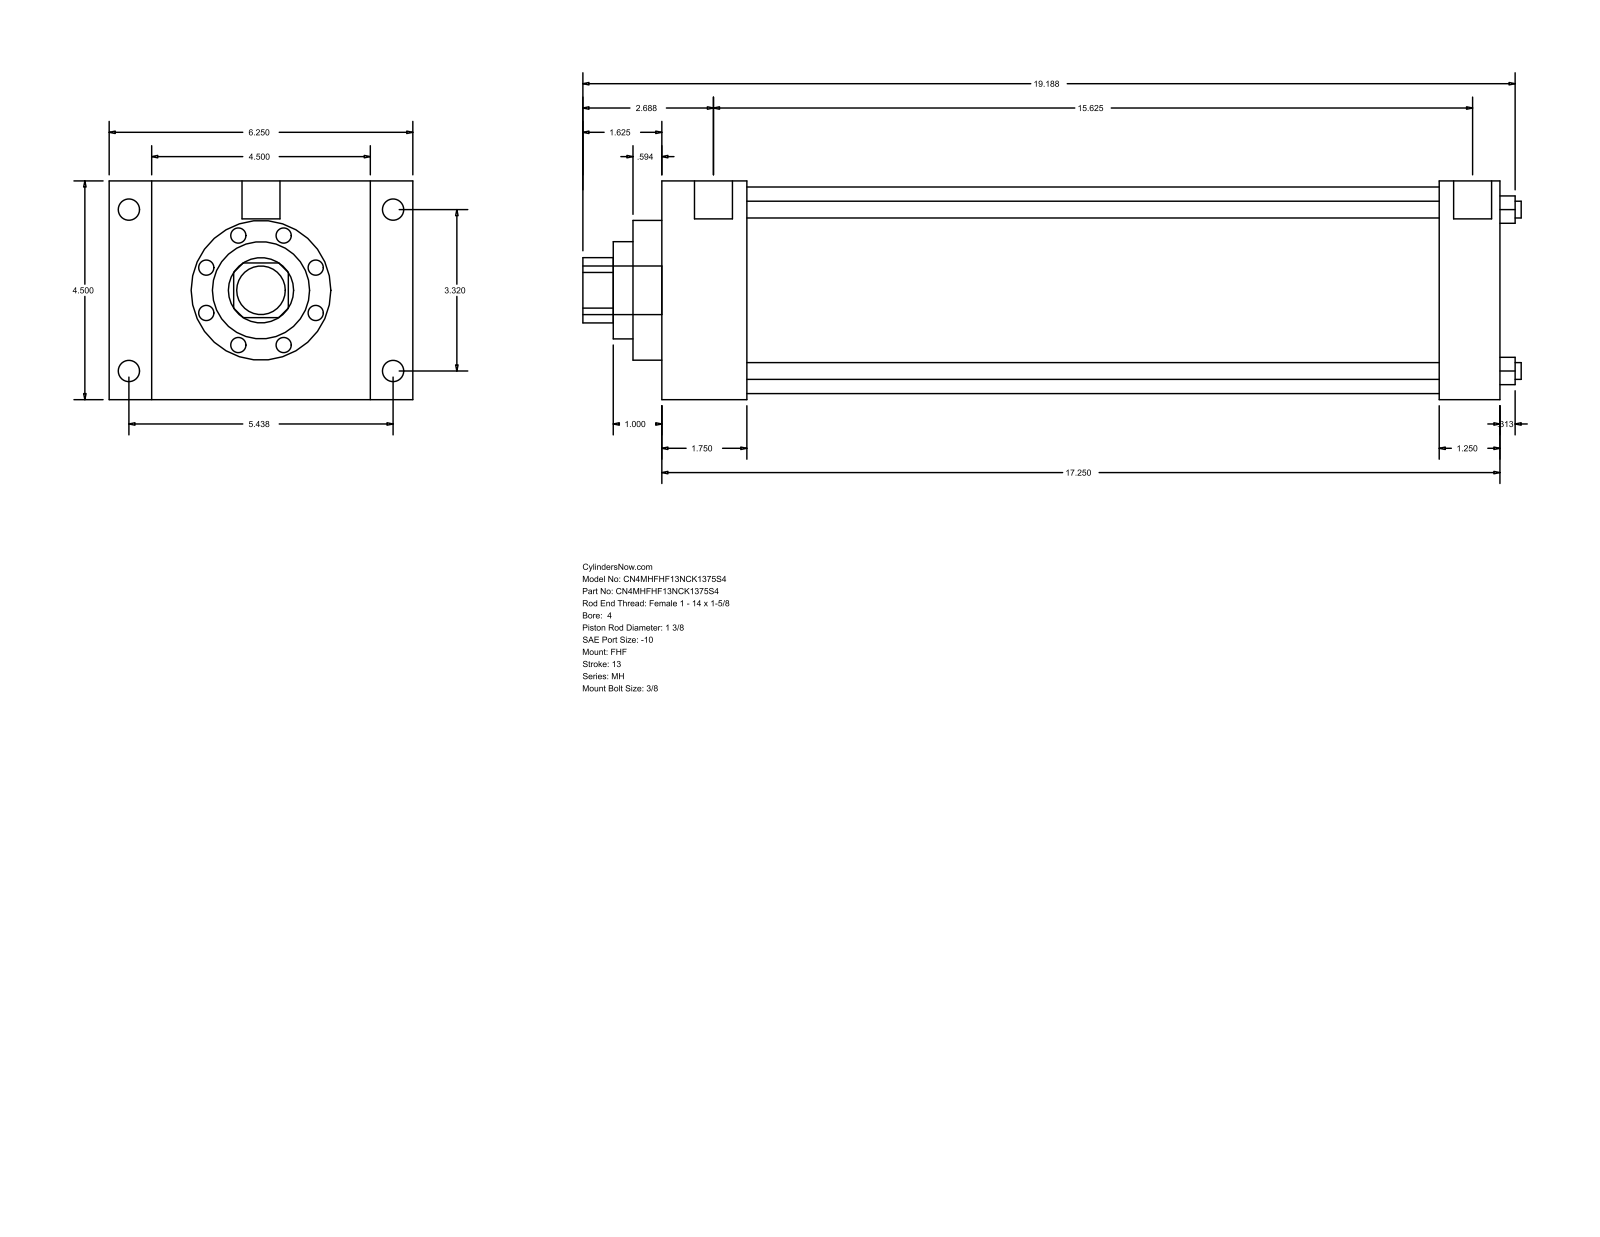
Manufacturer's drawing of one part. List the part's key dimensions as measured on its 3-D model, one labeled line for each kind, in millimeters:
Part name (STEP PRODUCT): MH_FHF__0400_1.375
STEP written by: GSSL Pune (CONFIG_CONTROL_DESIGN)
Units: millimetres
Bodies: 0 solids, 90 faces (61 planar, 29 cylindrical, 0 other)
Overall size (bounding box): 490.54 × 158.75 × 114.3
Round holes (diameter × count): ⌀8.76 ×4, ⌀34.92 ×1, ⌀50.8 ×1, ⌀73.03 ×1, ⌀107.95 ×1
Round bosses / shafts (diameter × count): ⌀11.13 ×4, ⌀8.73 ×4, ⌀19.84 ×2, ⌀25.4 ×1
Partial cylindrical surfaces — rounded edges, fillets, slot ends (radius × count): R17.06 ×1
Main face-to-face distances: 114.3, 438.16, 44.45, 393.71, 22.23, 136.53, 158.76, 406.41, 361.96, 31.75
Hole centre spacings: 59.62, 84.32, 119.25
